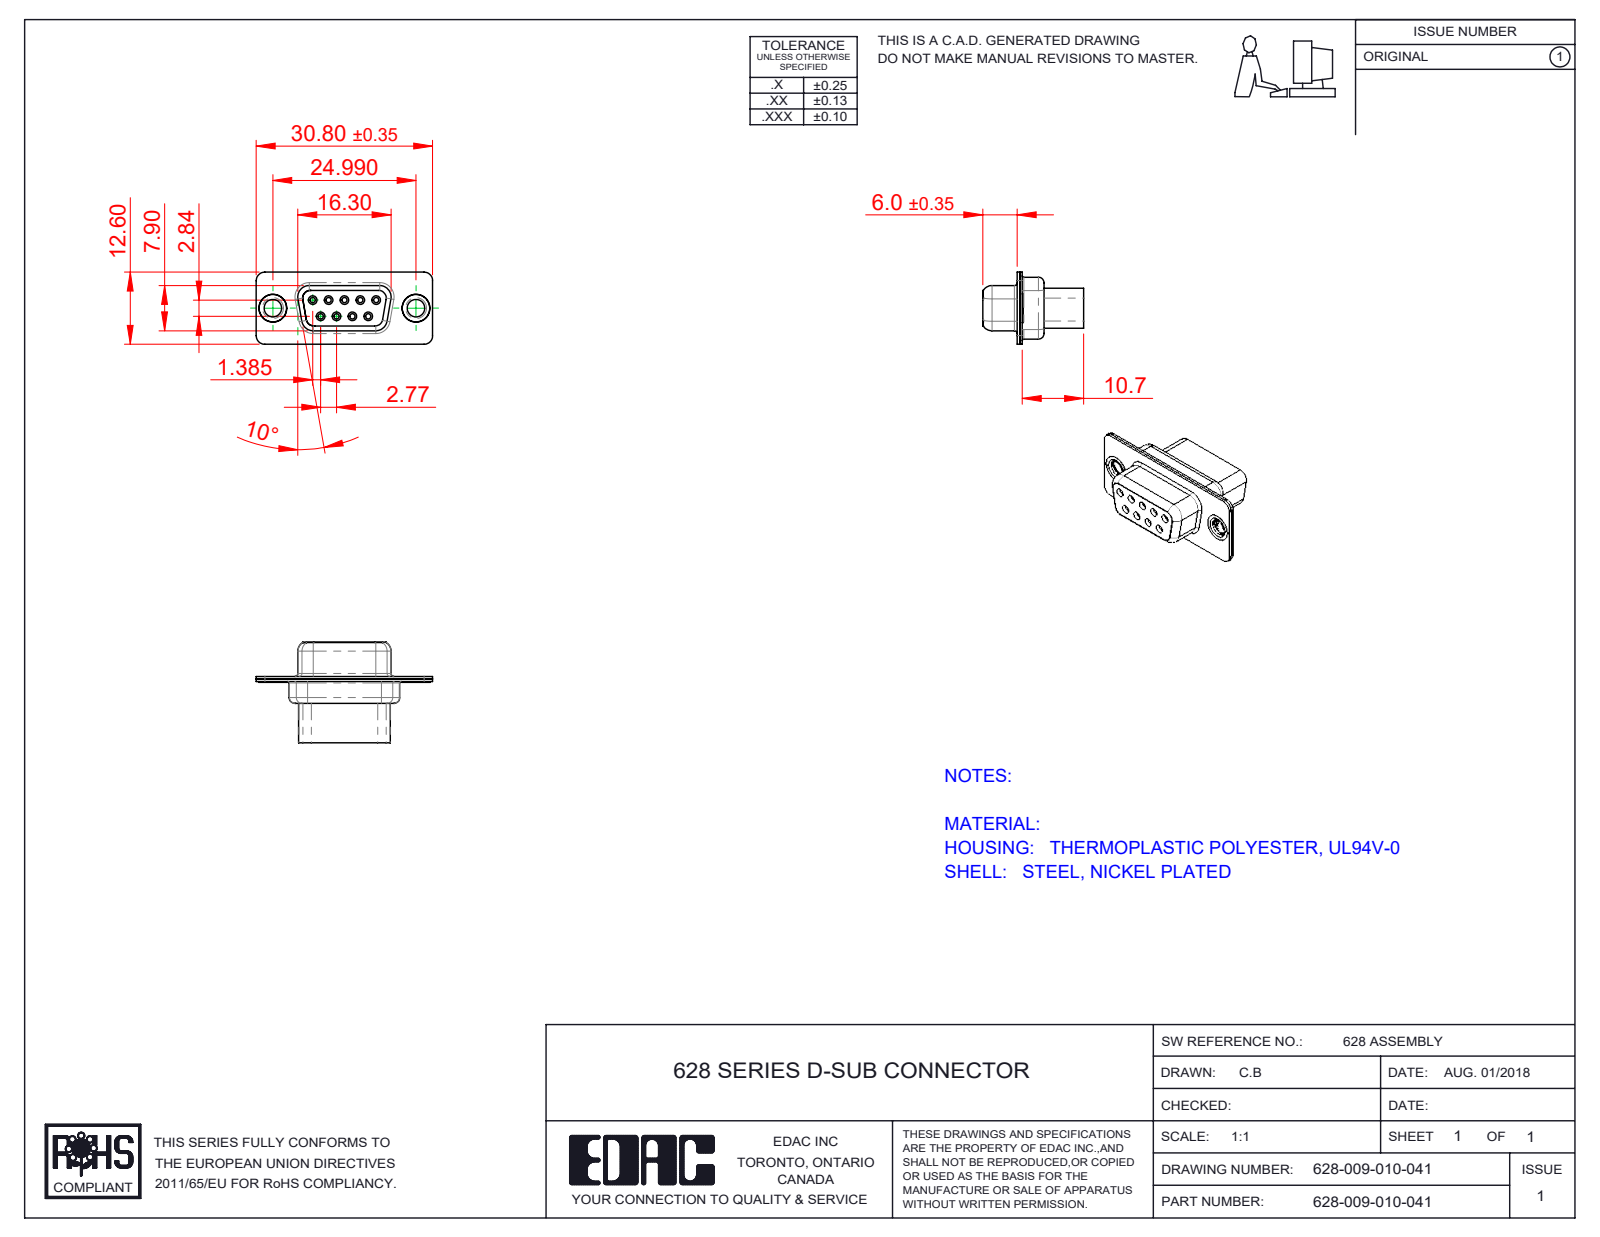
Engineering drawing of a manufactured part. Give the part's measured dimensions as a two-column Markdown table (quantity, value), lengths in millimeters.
| quantity | value |
| --- | --- |
| part name | 628 Shell Rear_09 Contacts; 628 Housing_09 HP; 628 Thru Hole Rivet; 628-009-010-241 (+1 more) |
| STEP written by | SolidWorks 2020 (CONFIG_CONTROL_DESIGN) |
| units | millimeters |
| bodies | 5 solids, 370 faces (94 planar, 193 cylindrical, 83 other) |
| overall size | 30.8 × 17.6 × 12.6 |
| volume | 2 043 mm³ |
| surface area | 3 923 mm² |
| round holes (diameter × count) | 0.9 × 9, 1.5 × 9, 2 × 9, 1.7 × 5, 1.6 × 4, 3.05 × 2, 4 × 2, 4.05 × 2, 4.85 × 2 |
| round bosses / shafts (diameter × count) | 5 × 2, 4.95 × 2, 4.8 × 2, 3.55 × 2 |
| partial cylindrical surfaces (radius × count) | 1.5 × 17, 2 × 12, 1.35 × 6, 0.25 × 4, 0.5 × 4, 0.6 × 4, 0.65 × 4, 0.95 × 4 |
| main face-to-face distances | 0.45, 0.4, 0.9, 6.6, 8.5, 1.9, 1.4, 7, 0.5, 7.05 |
| hole center spacings | 3.16, 2.77, 5.54, 5.03, 5.04, 8.31, 7.48, 7.49 |
